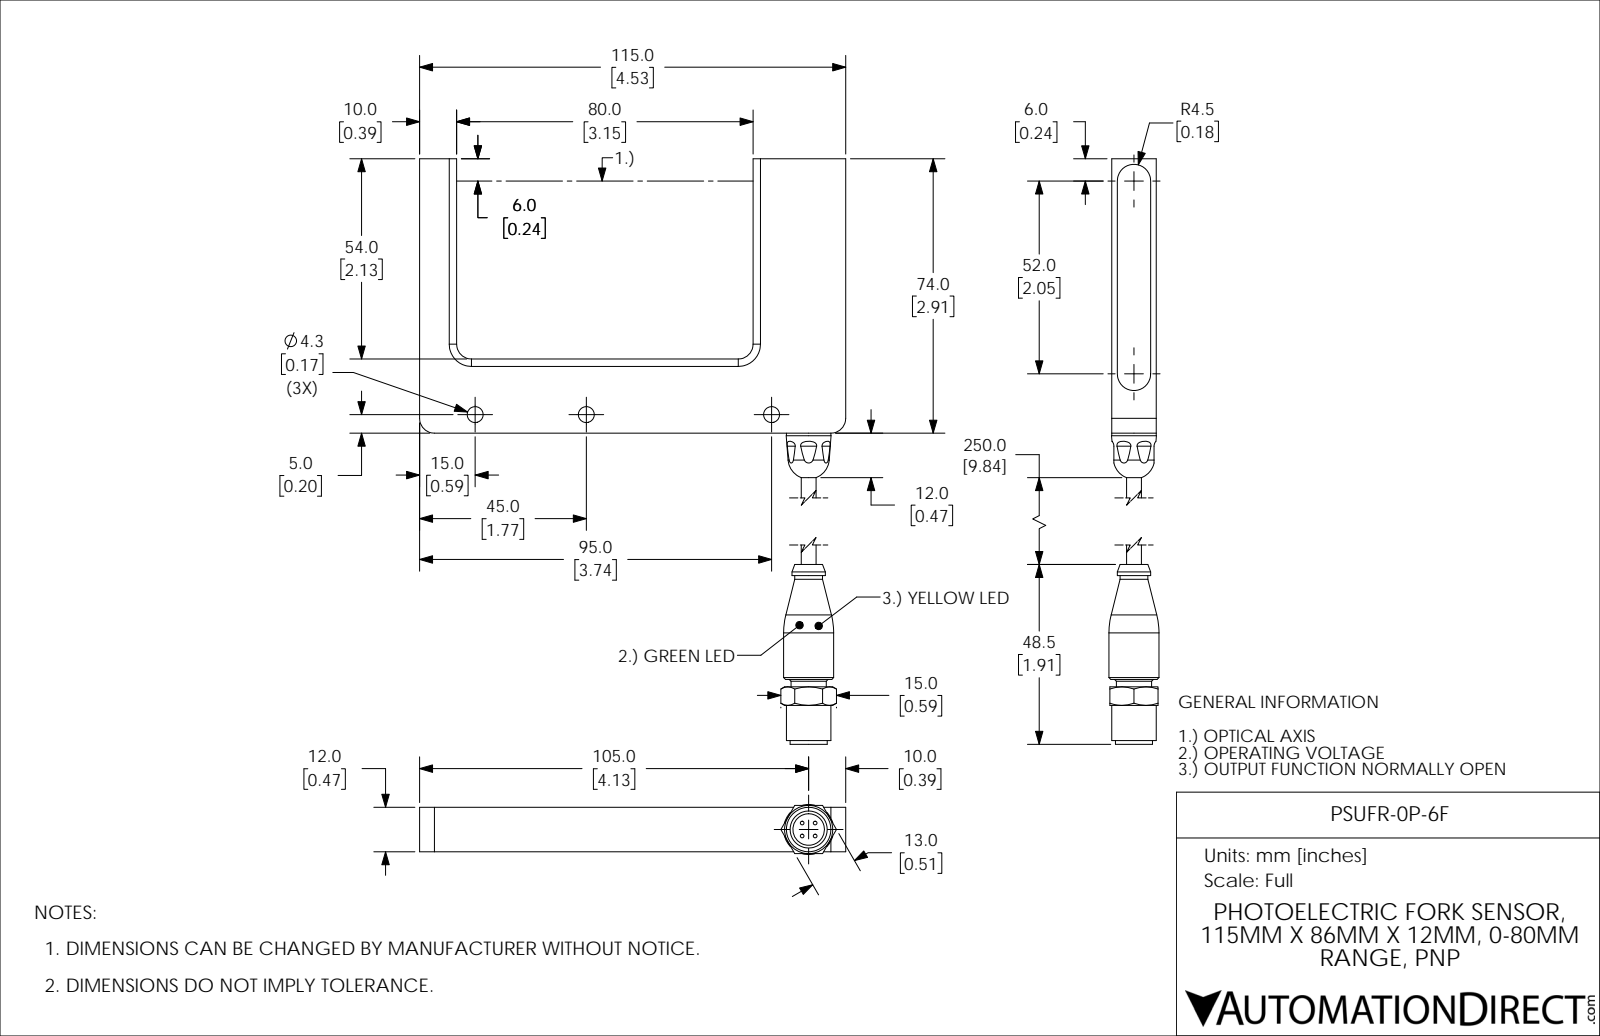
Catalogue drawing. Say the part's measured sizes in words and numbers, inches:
The part is named "PSUFR-0P-6F". Its 3-D file was written by "SolidWorks 2017 (AUTOMOTIVE_DESIGN)". It is 2 solids with 109 faces: 43 planar, 39 cylindrical and 27 other. Overall it measures 8.445 by 4.528 by 0.531 inches. Its volume is 3.405 cubic inches and its surface area 27.26 square inches. Round holes: 3 of diameter 0.169, 1 of diameter 0.173, 1 of diameter 0.335. Round bosses or shafts: 4 of diameter 0.039, 1 of diameter 0.531, 1 of diameter 0.472, 1 of diameter 0.394, 1 of diameter 0.374, 1 of diameter 0.354, 1 of diameter 0.295, 1 of diameter 0.157. Partial cylindrical surfaces (rounded edges, fillets, slot ends): 12 of radius 0.079, 4 of radius 0.157, 2 of radius 0.177. The main face-to-face distances are 0.472, 4.524, 0.787, 4.52, 2.126, 2.913, 0.98, 0.39, 3.539, 3.15. The hole center spacings are 1.181, 1.969, 3.15.
